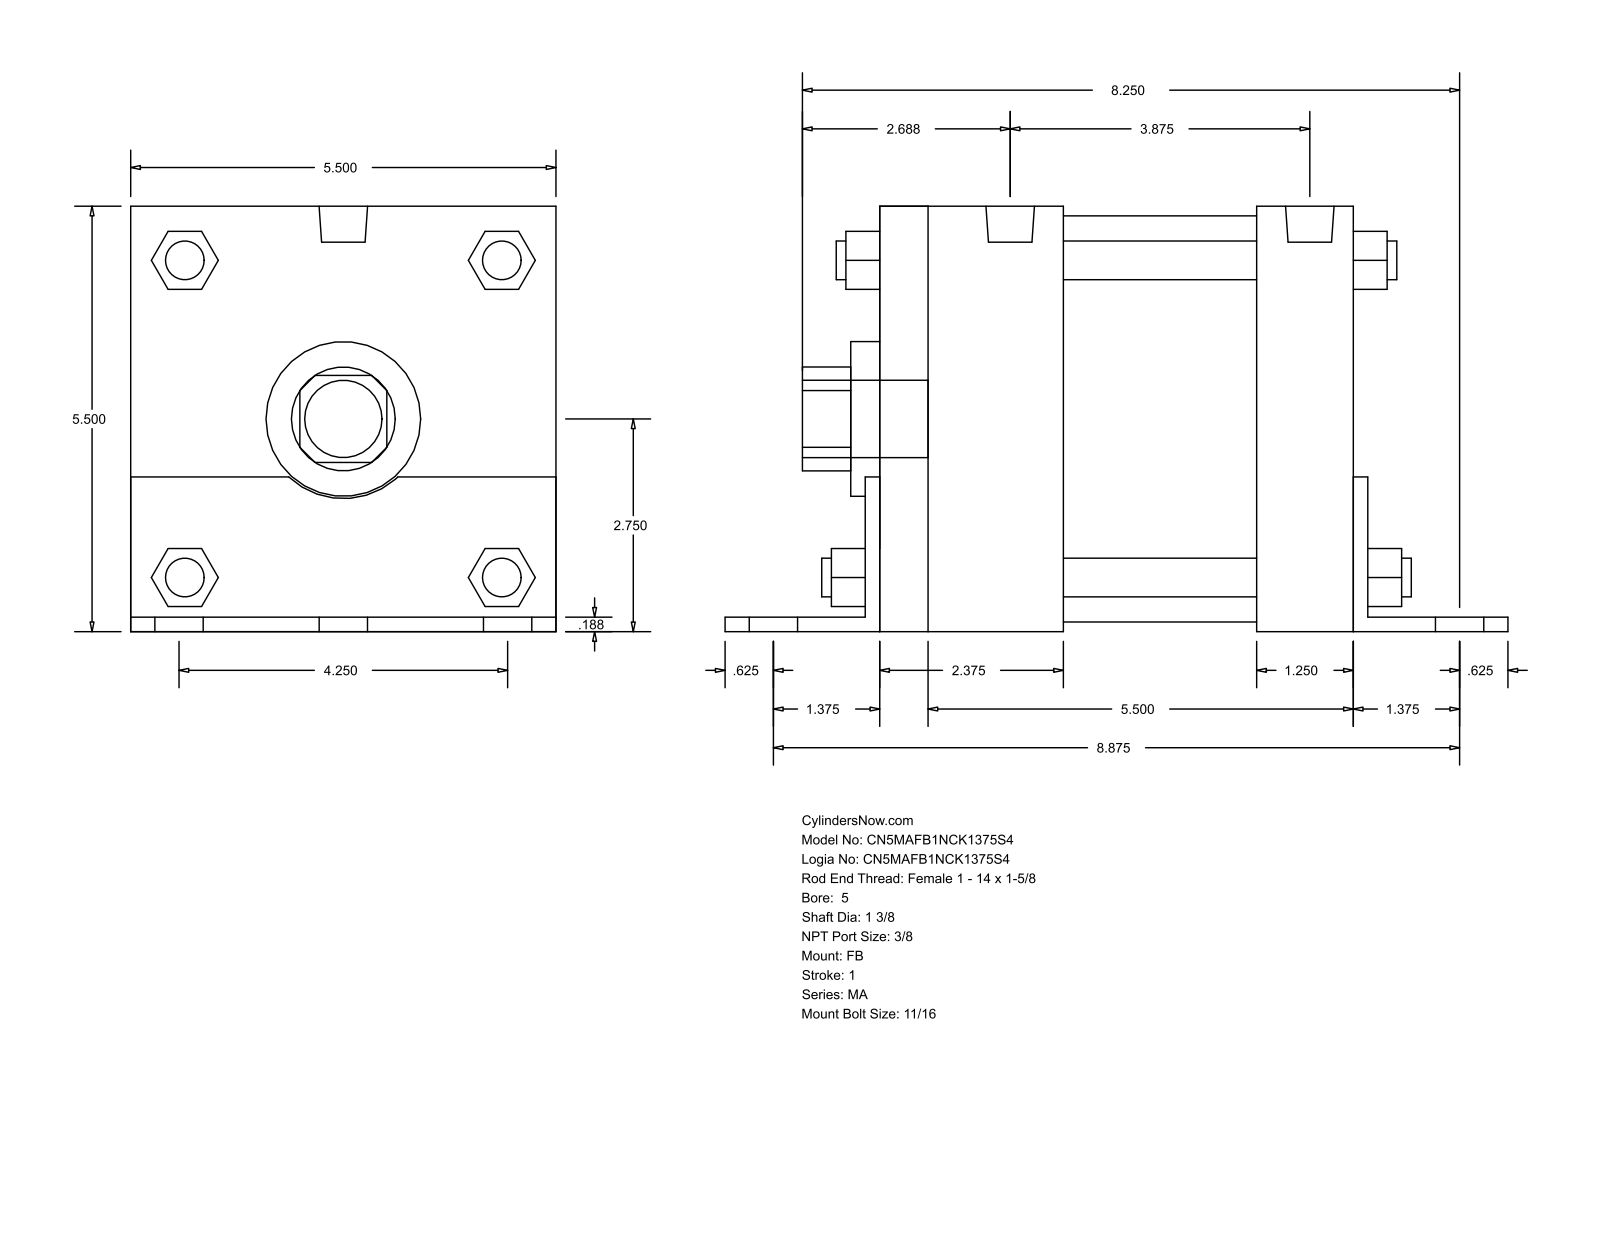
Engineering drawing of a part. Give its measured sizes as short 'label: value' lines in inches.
name: MA_FB__0500_1.375
written by: GSSL Pune (CONFIG_CONTROL_DESIGN)
unit: in
bodies: 0 solids, 140 faces (105 planar, 35 cylindrical, 0 other)
size: 10.125 × 5.502 × 5.5
holes: 1× ⌀1.375, 1× ⌀2, 1× ⌀5.25
bosses: 6× ⌀0.687, 4× ⌀0.5, 4× ⌀0.437, 2× ⌀0.627, 1× ⌀1
rounds: 1× R0.672, 1× R1.03
face distances: 5.5, 0.187, 5.502, 0.185, 5.315, 6.125, 0.188, 6.313, 6.312, 6.5
